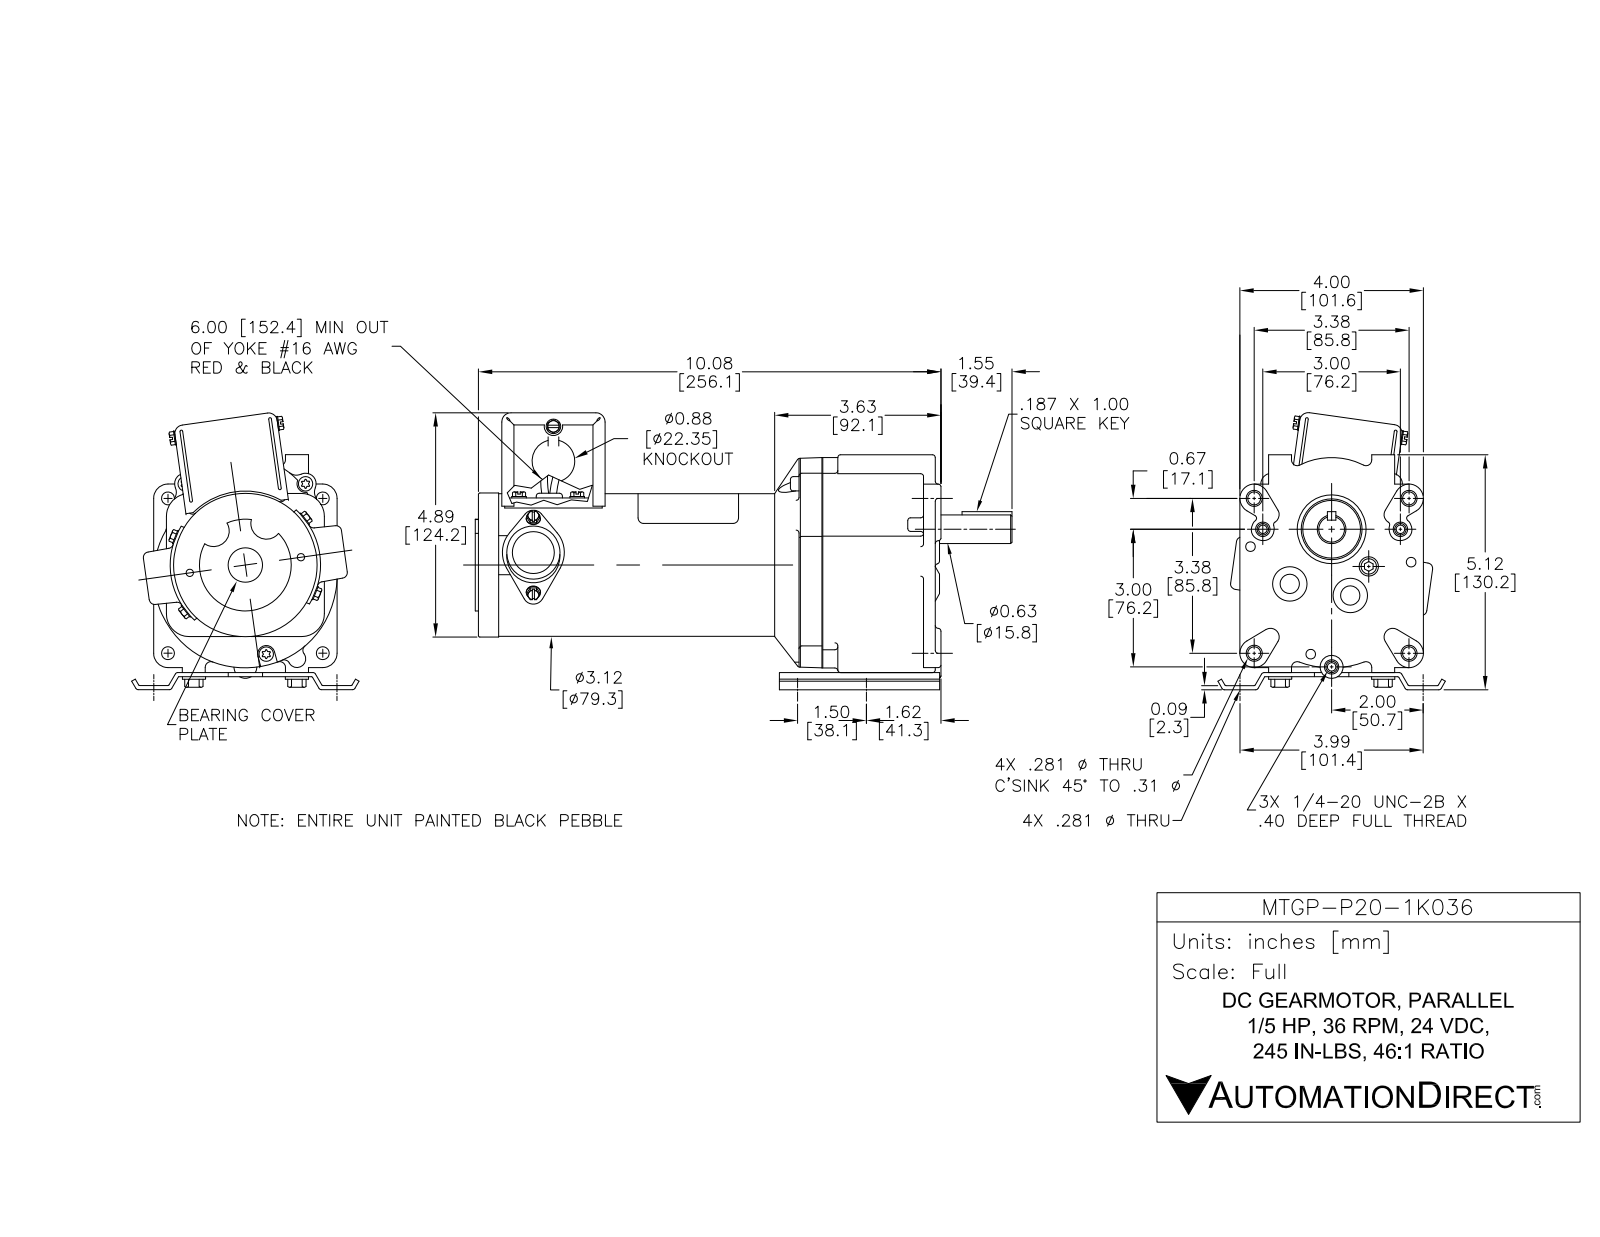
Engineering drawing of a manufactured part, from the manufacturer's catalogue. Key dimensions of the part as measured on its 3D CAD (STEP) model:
Part name (STEP PRODUCT): MTGP-P20-1K036
STEP written by: SolidWorks 2014 (AUTOMOTIVE_DESIGN)
Units: inches
Bodies: 53 solids, 984 faces (567 planar, 365 cylindrical, 52 other)
Overall size (bounding box): 11.698 × 6.209 × 4.939
Volume: 65.11 in³ · Surface area: 470.6 in²
Round holes (diameter × count): ⌀0.3 ×11, ⌀0.5 ×5, ⌀0.25 ×4, ⌀0.345 ×4, ⌀0.21 ×3, ⌀0.125 ×2, ⌀0.198 ×2, ⌀0.208 ×2, ⌀0.345 ×2, ⌀0.375 ×1, ⌀0.46 ×1, ⌀0.625 ×1
Round bosses / shafts (diameter × count): ⌀0.314 ×5, ⌀0.3 ×4, ⌀0.208 ×3, ⌀0.46 ×2, ⌀0.1 ×2, ⌀3.156 ×1, ⌀1.325 ×1, ⌀0.625 ×1
Partial cylindrical surfaces — rounded edges, fillets, slot ends (radius × count): R0.019 ×28, R0.1 ×23, R0.025 ×8, R0.25 ×7, R0.159 ×4, R0.19 ×4, R0.191 ×4, R0.234 ×4
Main face-to-face distances: 1.375, 3.495, 2.12, 0.09, 0.031, 0.25, 0.063, 0.05, 1.425, 3.545
Hole centre spacings: 1.62, 1.23, 1.5, 1.504, 1.603, 2.974, 3.375, 6.911
